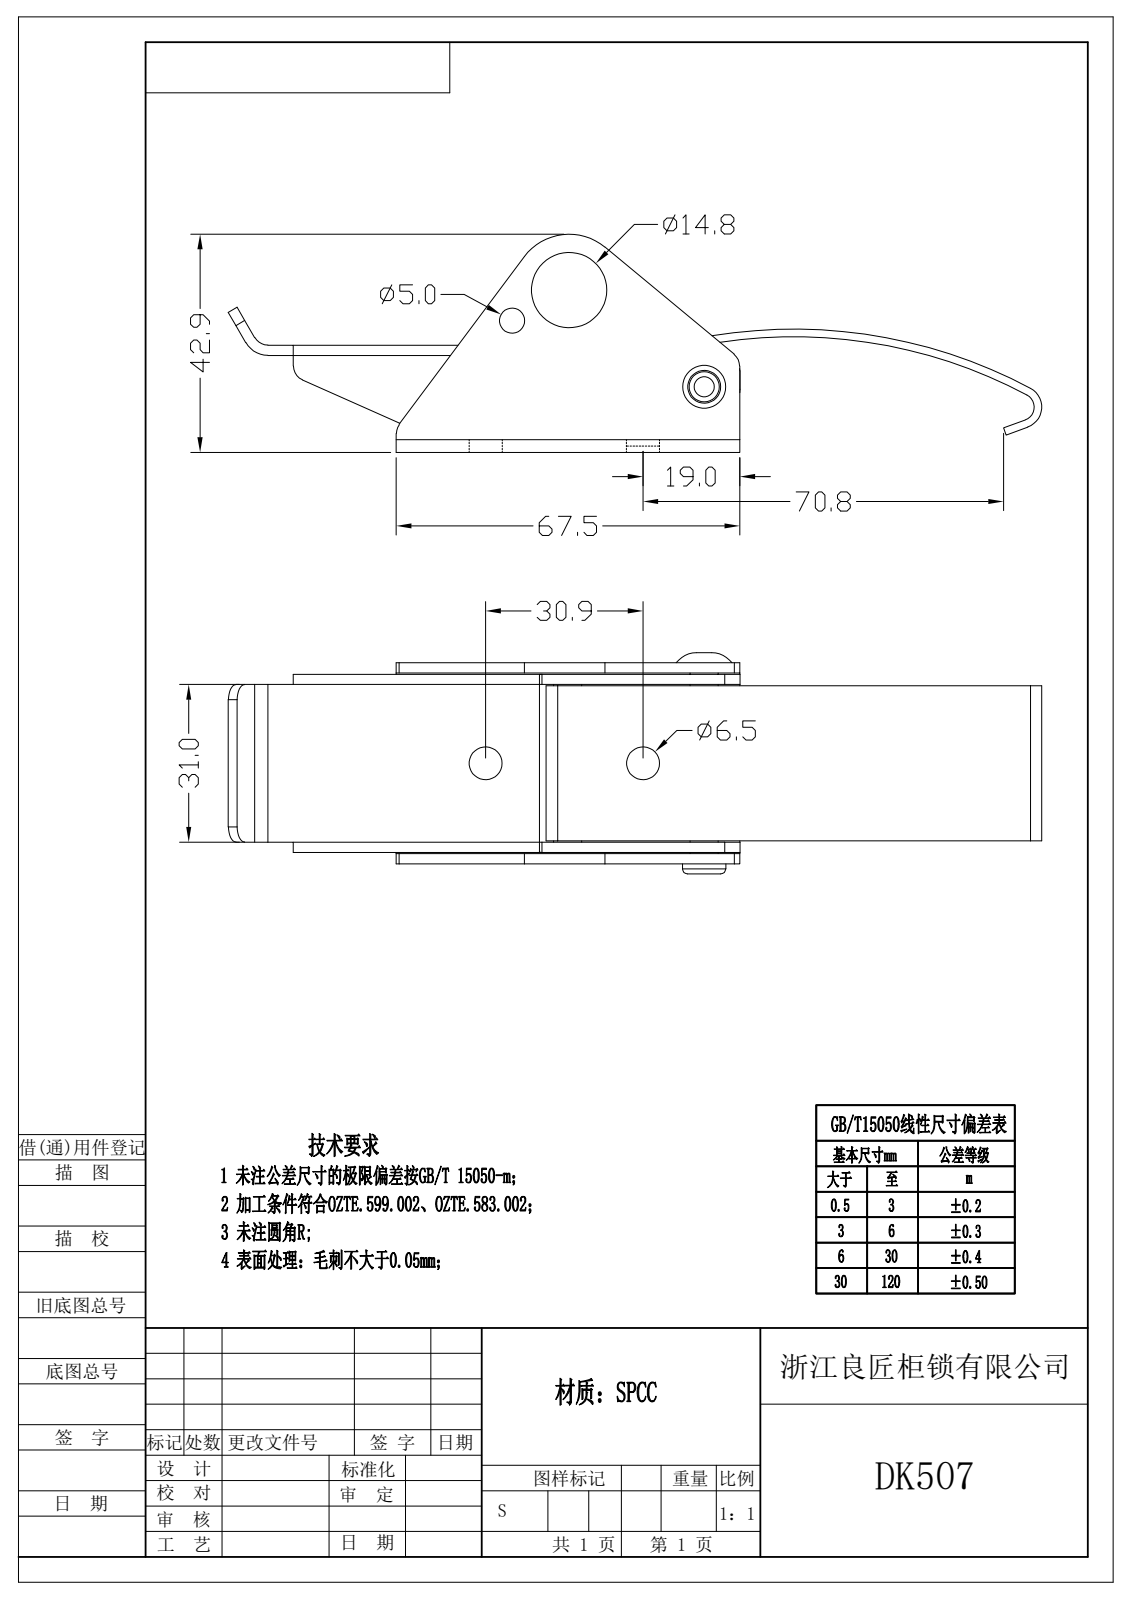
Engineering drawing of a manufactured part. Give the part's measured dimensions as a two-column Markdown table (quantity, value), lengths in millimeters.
| quantity | value |
| --- | --- |
| STEP written by | Rhino 8.5 (CONFIG_CONTROL_DESIGN) |
| units | millimeters |
| bodies | 5 solids, 173 faces (61 planar, 82 cylindrical, 30 other) |
| overall size | 159.93 × 43.43 × 42.73 |
| volume | 24 855 mm³ |
| surface area | 32 236 mm² |
| round holes (diameter × count) | 6.5 × 2, 5 × 1, 5.7 × 1, 6 × 1, 14.8 × 1 |
| round bosses / shafts (diameter × count) | 5.5 × 2, 8.5 × 1, 5.7 × 1 |
| partial cylindrical surfaces (radius × count) | 3 × 5, 2 × 4, 0.5 × 2, 1 × 2, 2.5 × 2, 5 × 1, 6.5 × 1, 8.31 × 1 |
| main face-to-face distances | 2, 2.25, 35.25, 19.04, 37.5, 33, 37.25, 4.25, 33.25, 21.04 |
| hole center spacings | 12.74, 20.19, 22.84, 27.1, 30.9, 32.42, 39.88 |
